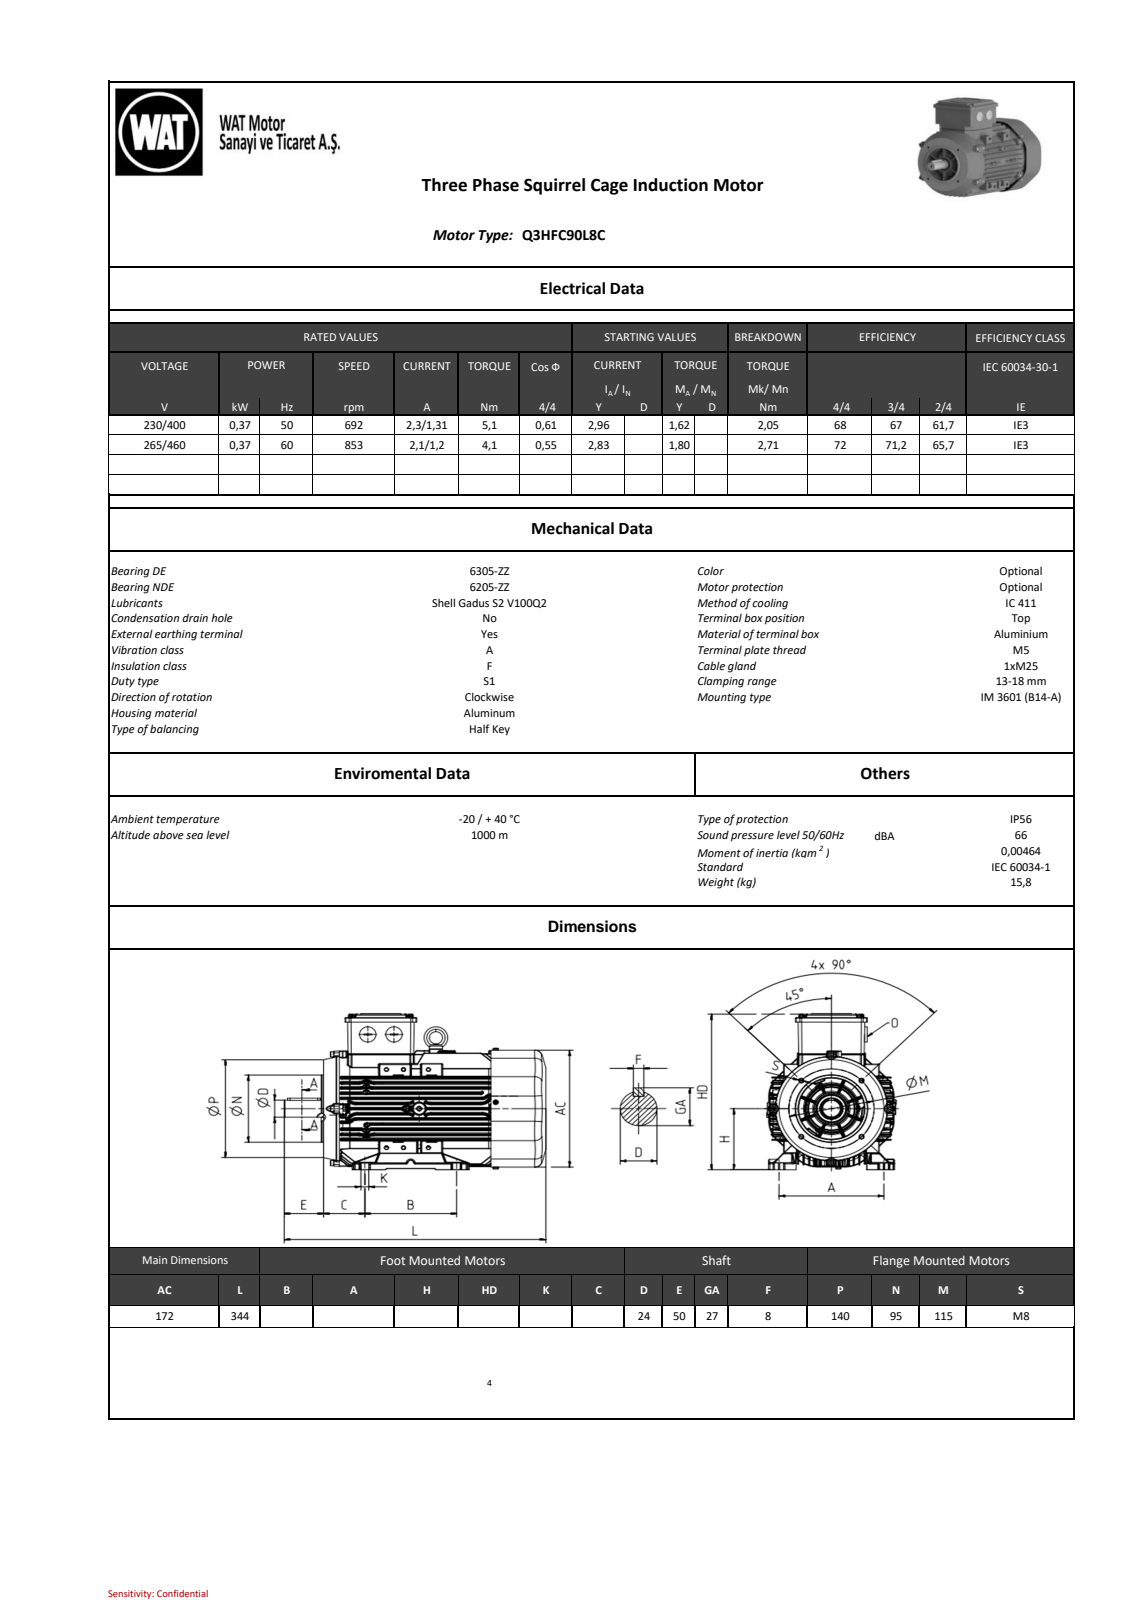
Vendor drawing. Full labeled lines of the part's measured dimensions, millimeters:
Part name (STEP PRODUCT): model1
STEP written by: SIEMENS PLM Software NX2206.8101 (AUTOMOTIVE_DESIGN)
Units: millimetres
Bodies: 0 solids, 5090 faces (1296 planar, 2199 cylindrical, 1595 other)
Overall size (bounding box): 343.54 × 219.57 × 178.35
Round holes (diameter × count): ⌀6.8 ×4, ⌀9.87 ×1, ⌀37.42 ×1, ⌀68 ×1, ⌀79.79 ×1, ⌀97.79 ×1, ⌀115.78 ×1
Round bosses / shafts (diameter × count): ⌀5 ×8, ⌀8 ×7, ⌀10 ×5, ⌀25 ×3, ⌀102.19 ×1, ⌀95 ×1, ⌀84.19 ×1, ⌀39.5 ×1
Partial cylindrical surfaces — rounded edges, fillets, slot ends (radius × count): R1 ×621, R0.8 ×541, R2 ×79, R0.5 ×62, R0.5 ×48, R8 ×28, R4 ×10, R5.68 ×7
Main face-to-face distances: 7.5, 91.91, 8.93, 82.98, 23.57, 50.35, 7.37, 9.06, 90.35, 75.04
Hole centre spacings: 57.42, 57.5, 57.51, 57.59, 81.32, 81.33, 115.01, 57.45
